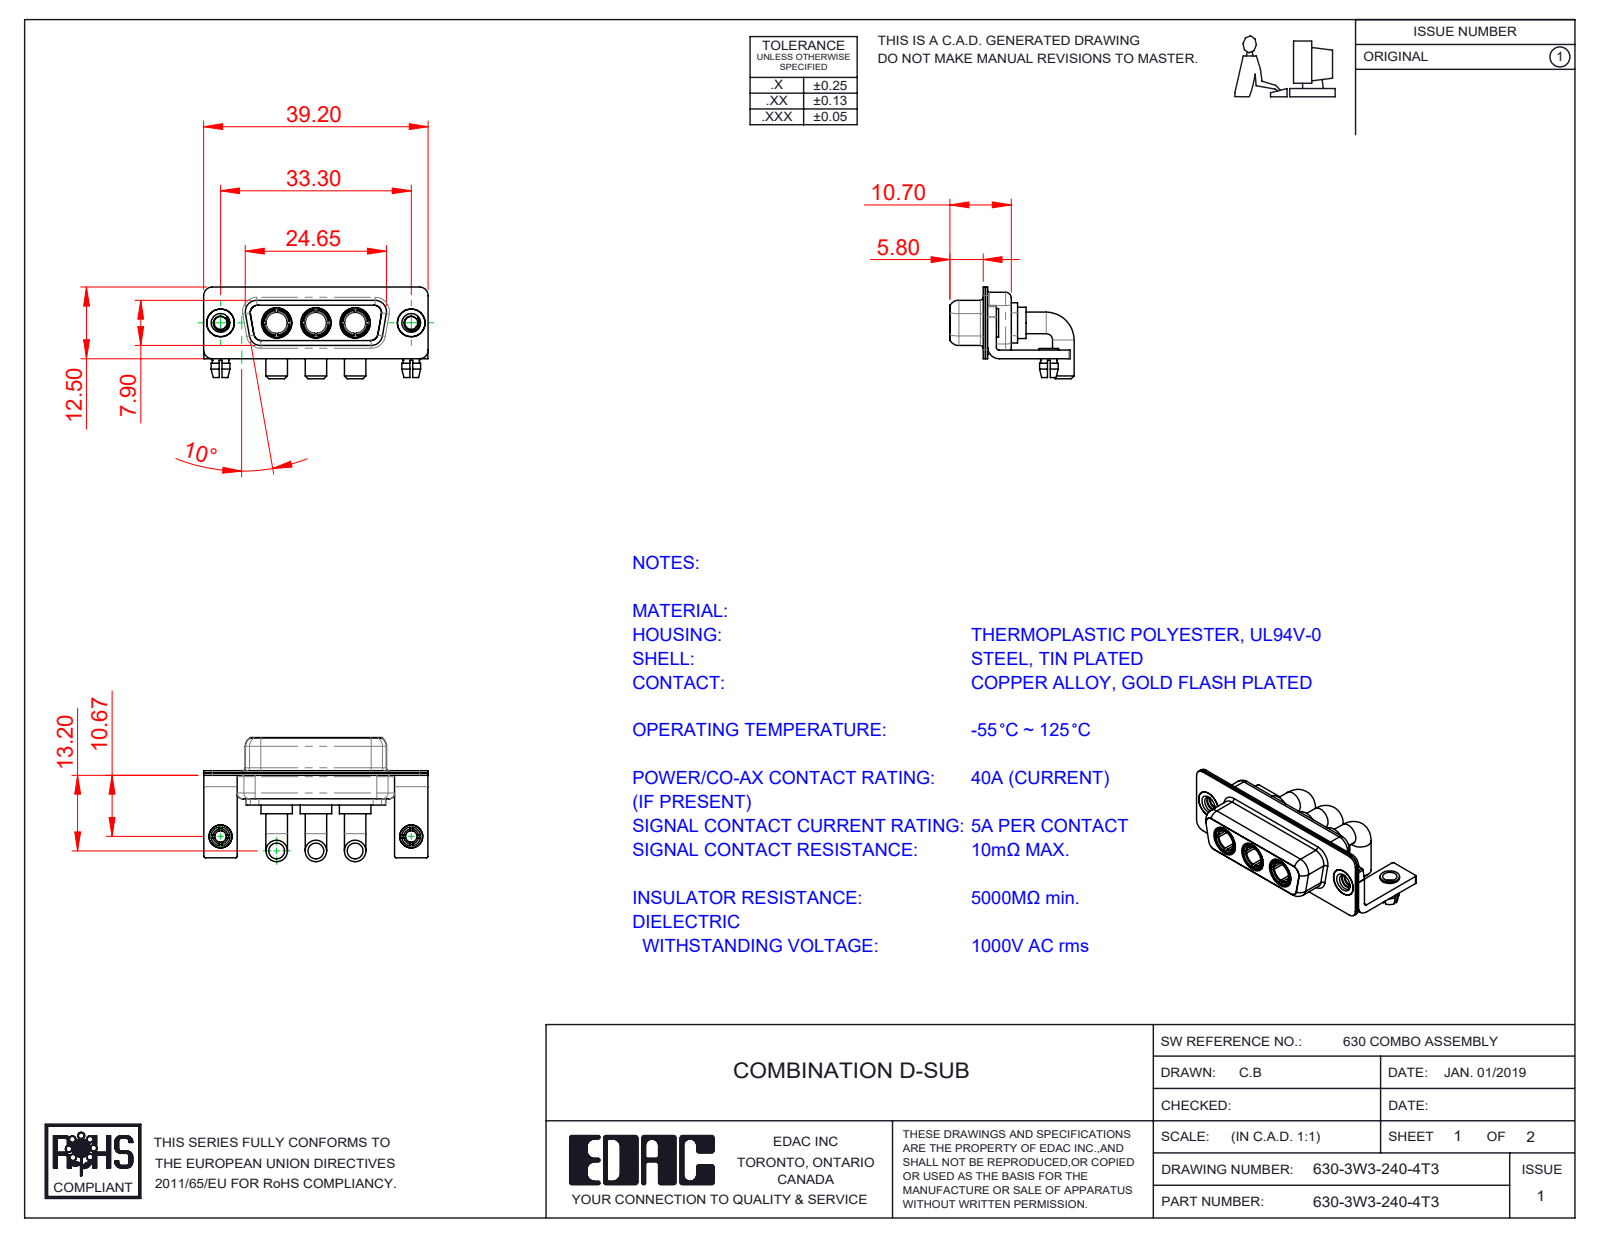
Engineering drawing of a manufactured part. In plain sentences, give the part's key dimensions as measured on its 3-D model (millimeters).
The part is named "630Combo Shell Front_15 Contacts; 630-3W3-240-4T3; 630Combo Shell Rear_15 Contacts; Power Socket_40A RA (+4 more)". Its 3-D file was written by "SolidWorks 2020 (CONFIG_CONTROL_DESIGN)". It is 15 solids with 645 faces: 222 planar, 262 cylindrical and 161 other. Overall it measures 39.2 by 21.68 by 16 millimeters. Its volume is 3 164 cubic millimeters and its surface area 6 853 square millimeters. Round holes: 5 of diameter 4.85, 3 of diameter 3.7, 3 of diameter 5.3, 2 of diameter 2, 2 of diameter 2.26, 2 of diameter 2.5, 2 of diameter 3.2, 2 of diameter 4, 2 of diameter 4.05. Round bosses or shafts: 6 of diameter 3.75, 3 of diameter 5.5, 3 of diameter 5.2, 3 of diameter 4.96, 3 of diameter 4.75, 2 of diameter 5, 2 of diameter 4.95, 2 of diameter 4.8. Partial cylindrical surfaces (rounded edges, fillets, slot ends): 16 of radius 0.25, 16 of radius 1.5, 13 of radius 2, 12 of radius 1.35, 8 of radius 1.6, 5 of radius 0.5, 4 of radius 0.6, 4 of radius 0.65. The main face-to-face distances are 0.4, 0.8, 1.4, 0.45, 1.5, 8.45, 1.8, 8.9, 6.2, 7.05. The hole center spacings are 6.85, 9.8, 16.65, 23.5, 33.3, 13.7.
